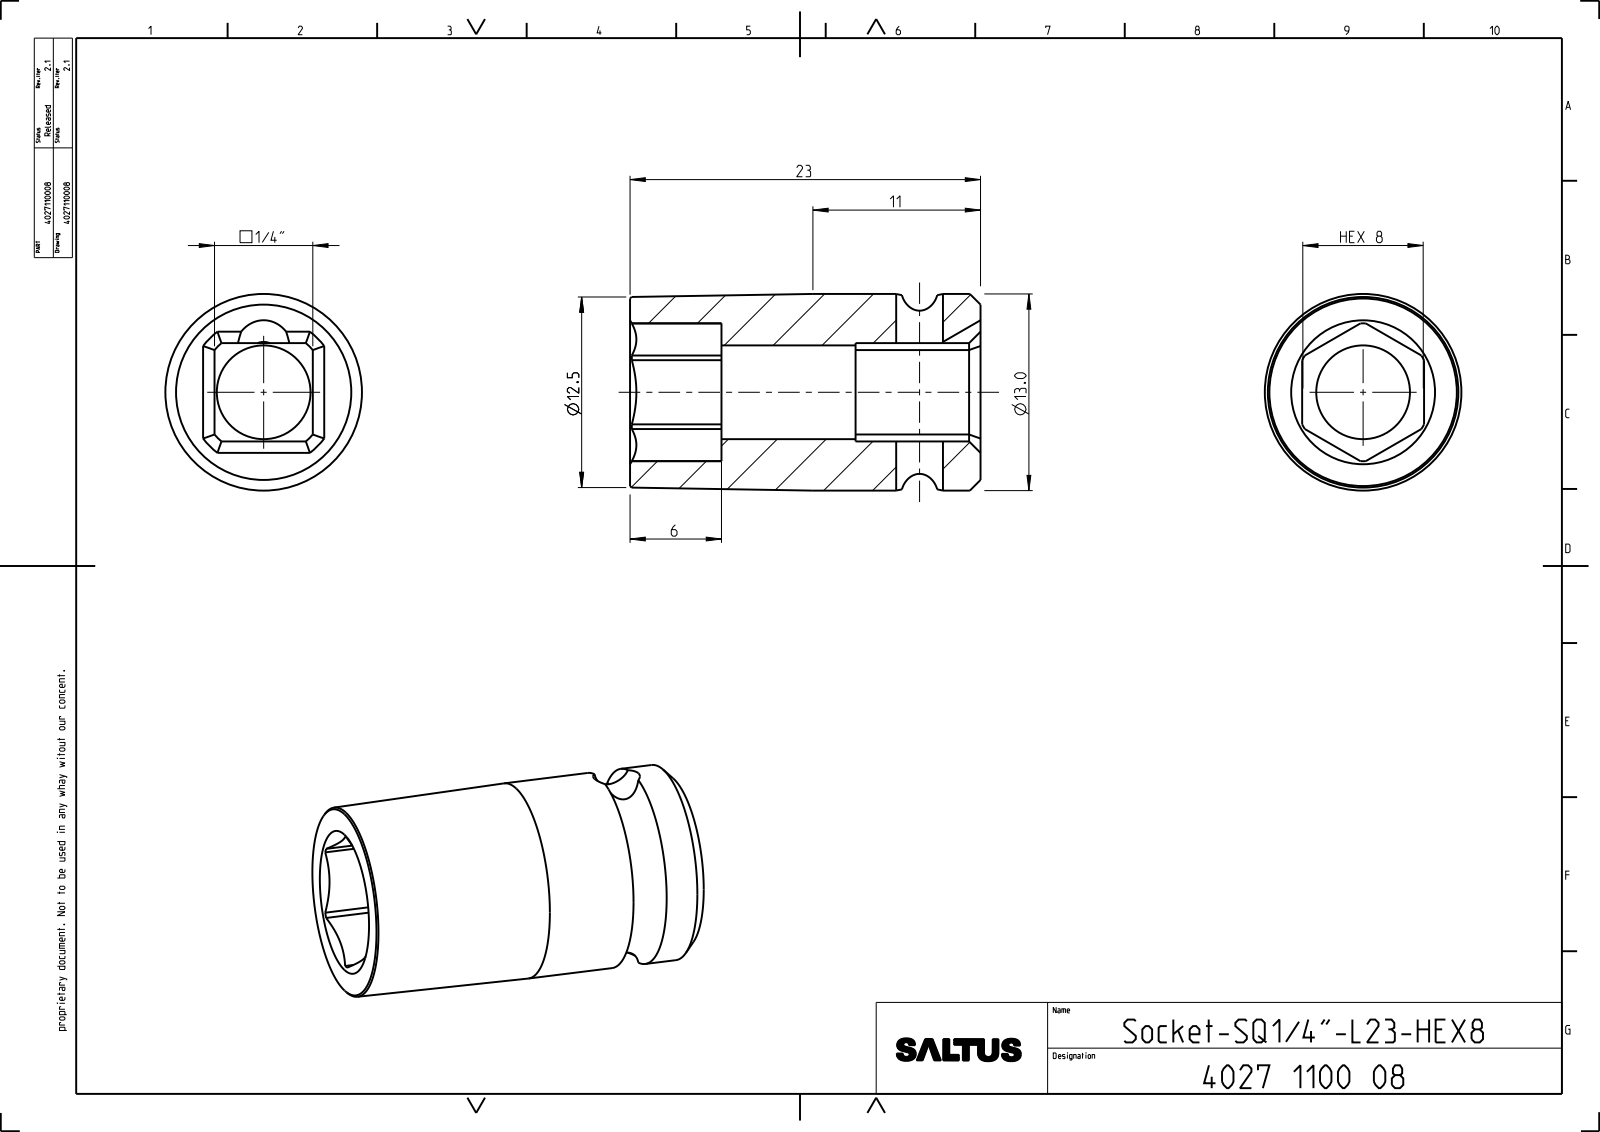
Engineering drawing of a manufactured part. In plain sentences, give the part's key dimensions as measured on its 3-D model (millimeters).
The part is named "4027110008". Its 3-D file was written by "CREO PARAMETRIC BY PTC INC, 2022414 (CONFIG_CONTROL_DESIGN)". It is 1 solid with 54 faces: 19 planar, 21 cylindrical and 14 other. Overall it measures 23 by 12.9 by 12.9 millimeters. Its volume is 1 908 cubic millimeters and its surface area 1 662 square millimeters. Round holes: 1 of diameter 3.07, 1 of diameter 6.15. Round bosses or shafts: 1 of diameter 12.9. Partial cylindrical surfaces (rounded edges, fillets, slot ends): 1 of radius 2, 1 of radius 4.25, 1 of radius 4.52. The main face-to-face distances are 8, 6.46, 0.77, 7.23, 23, 17, 6, 8.2, 8.8, 14.8.
